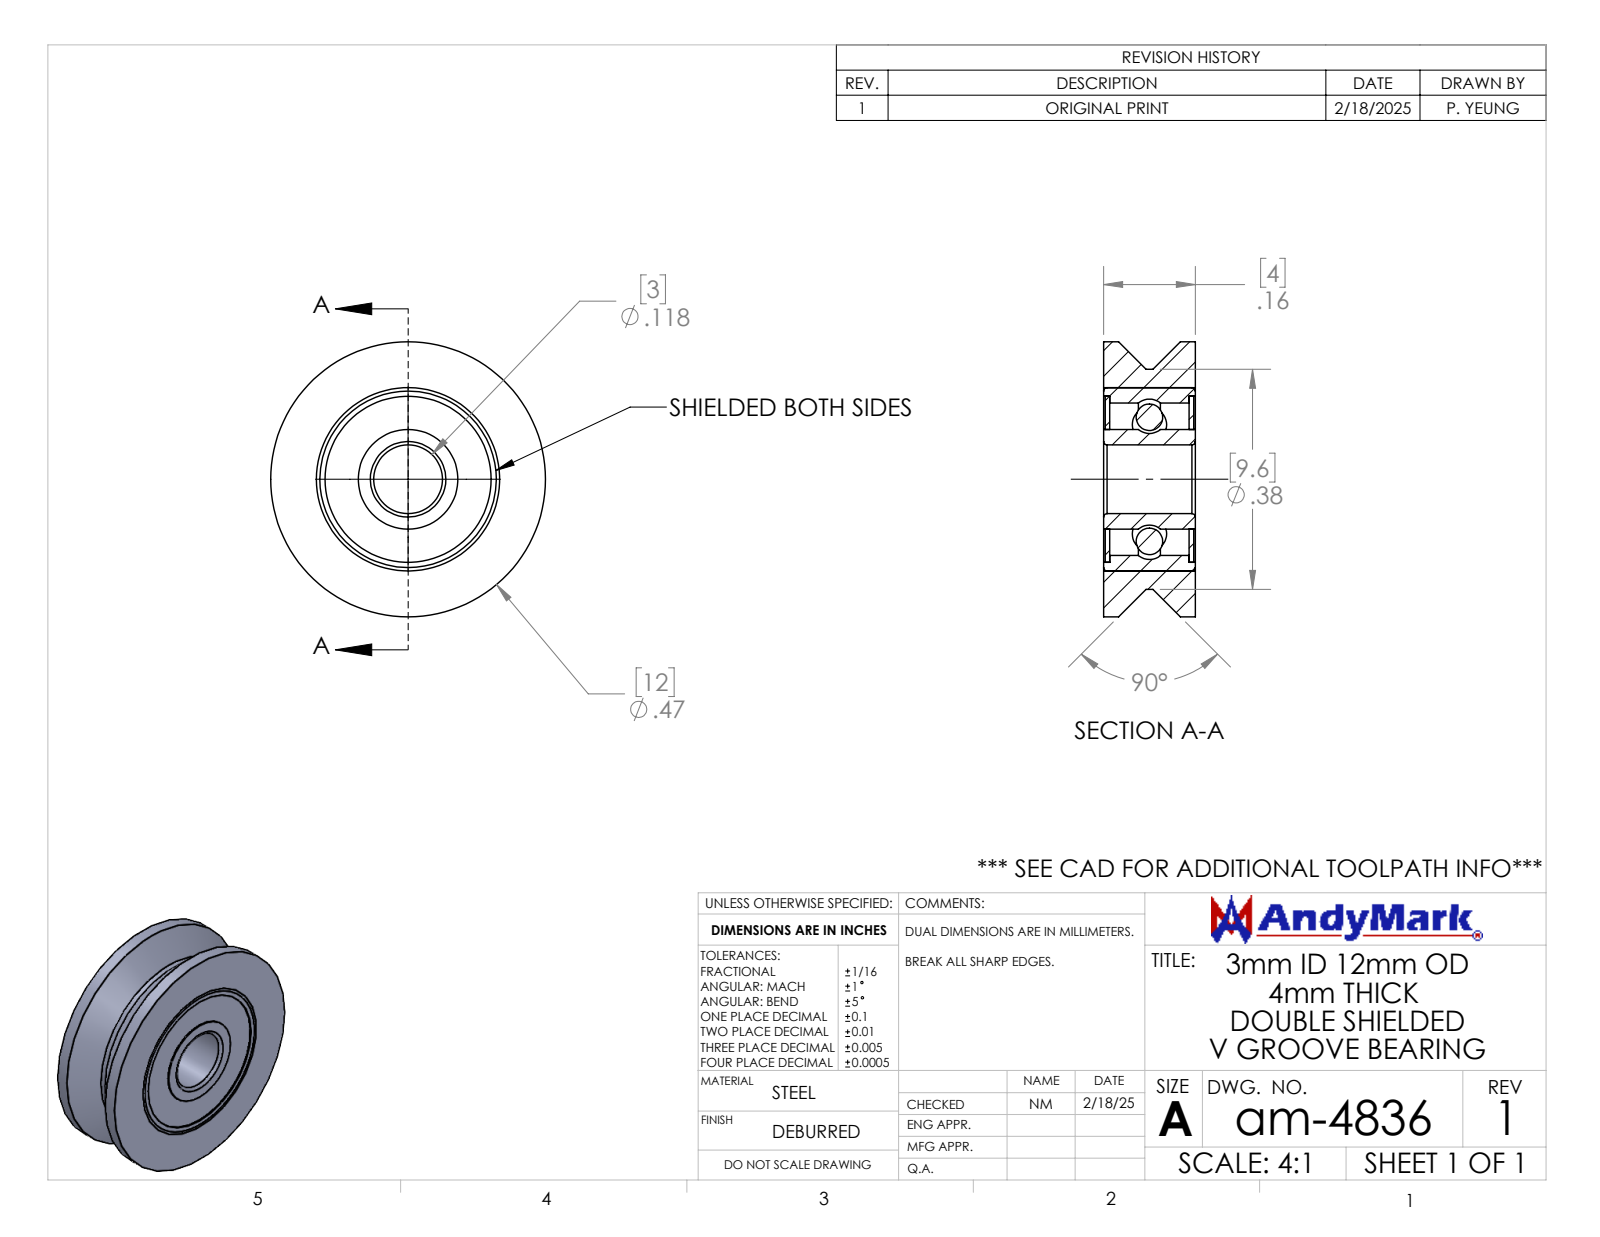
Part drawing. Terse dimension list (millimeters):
name: am-4836 3mm ID x 12mm OD x 4mm Thick V Groove Bearing
written by: SolidWorks 2024 (AUTOMOTIVE_DESIGN)
unit: mm
bodies: 14 solids, 80 faces (12 planar, 32 cylindrical, 36 other)
size: 12 × 12 × 4
volume: 301 mm³; area: 907 mm²
holes: 1× ⌀3, 1× ⌀4.35, 1× ⌀6.65, 1× ⌀7.25, 1× ⌀8
bosses: 1× ⌀12, 1× ⌀9.6
face distances: 4, 3.73, 3.93, 3.66, 3.46, 3.86
